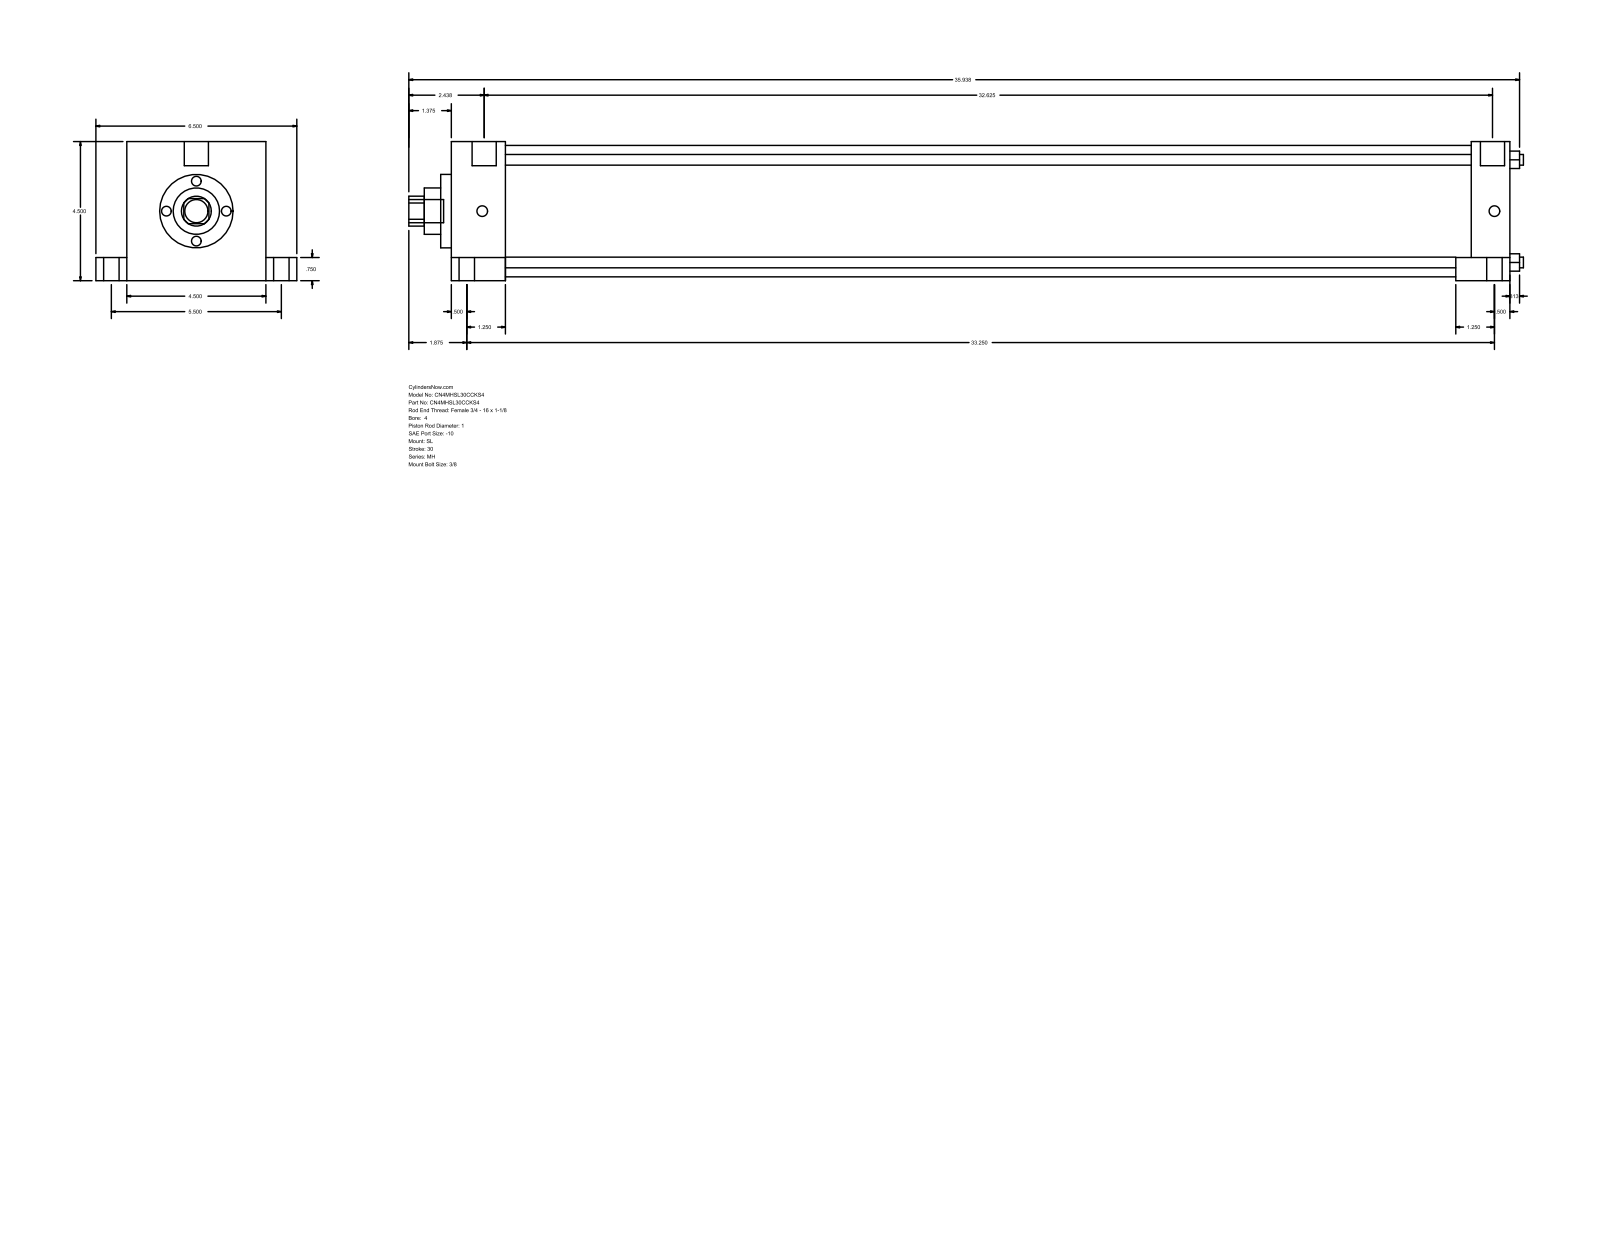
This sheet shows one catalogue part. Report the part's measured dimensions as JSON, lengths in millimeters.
{"part_name": "MH_SL__0400_1", "step_written_by": "GSSL Pune (CONFIG_CONTROL_DESIGN)", "units": "millimeters", "bodies": {"solids": 0, "faces": 110, "planar": 77, "cylindrical": 33, "other": 0}, "overall_size": [915.99, 165.1, 114.3], "round_holes": [[8.76, 4], [25.4, 1], [38.1, 1], [60.33, 1], [107.95, 1]], "round_bosses_or_shafts": [[19.05, 5], [12.7, 4], [8.73, 4], [19.84, 2]], "partial_cylinders_radius": [[12.29, 1]], "face_to_face_distances": [114.3, 869.96, 44.46, 825.5, 838.2, 793.74, 31.76, 25.4, 139.7, 19.05], "hole_center_spacings": [59.62, 84.32, 119.25]}
